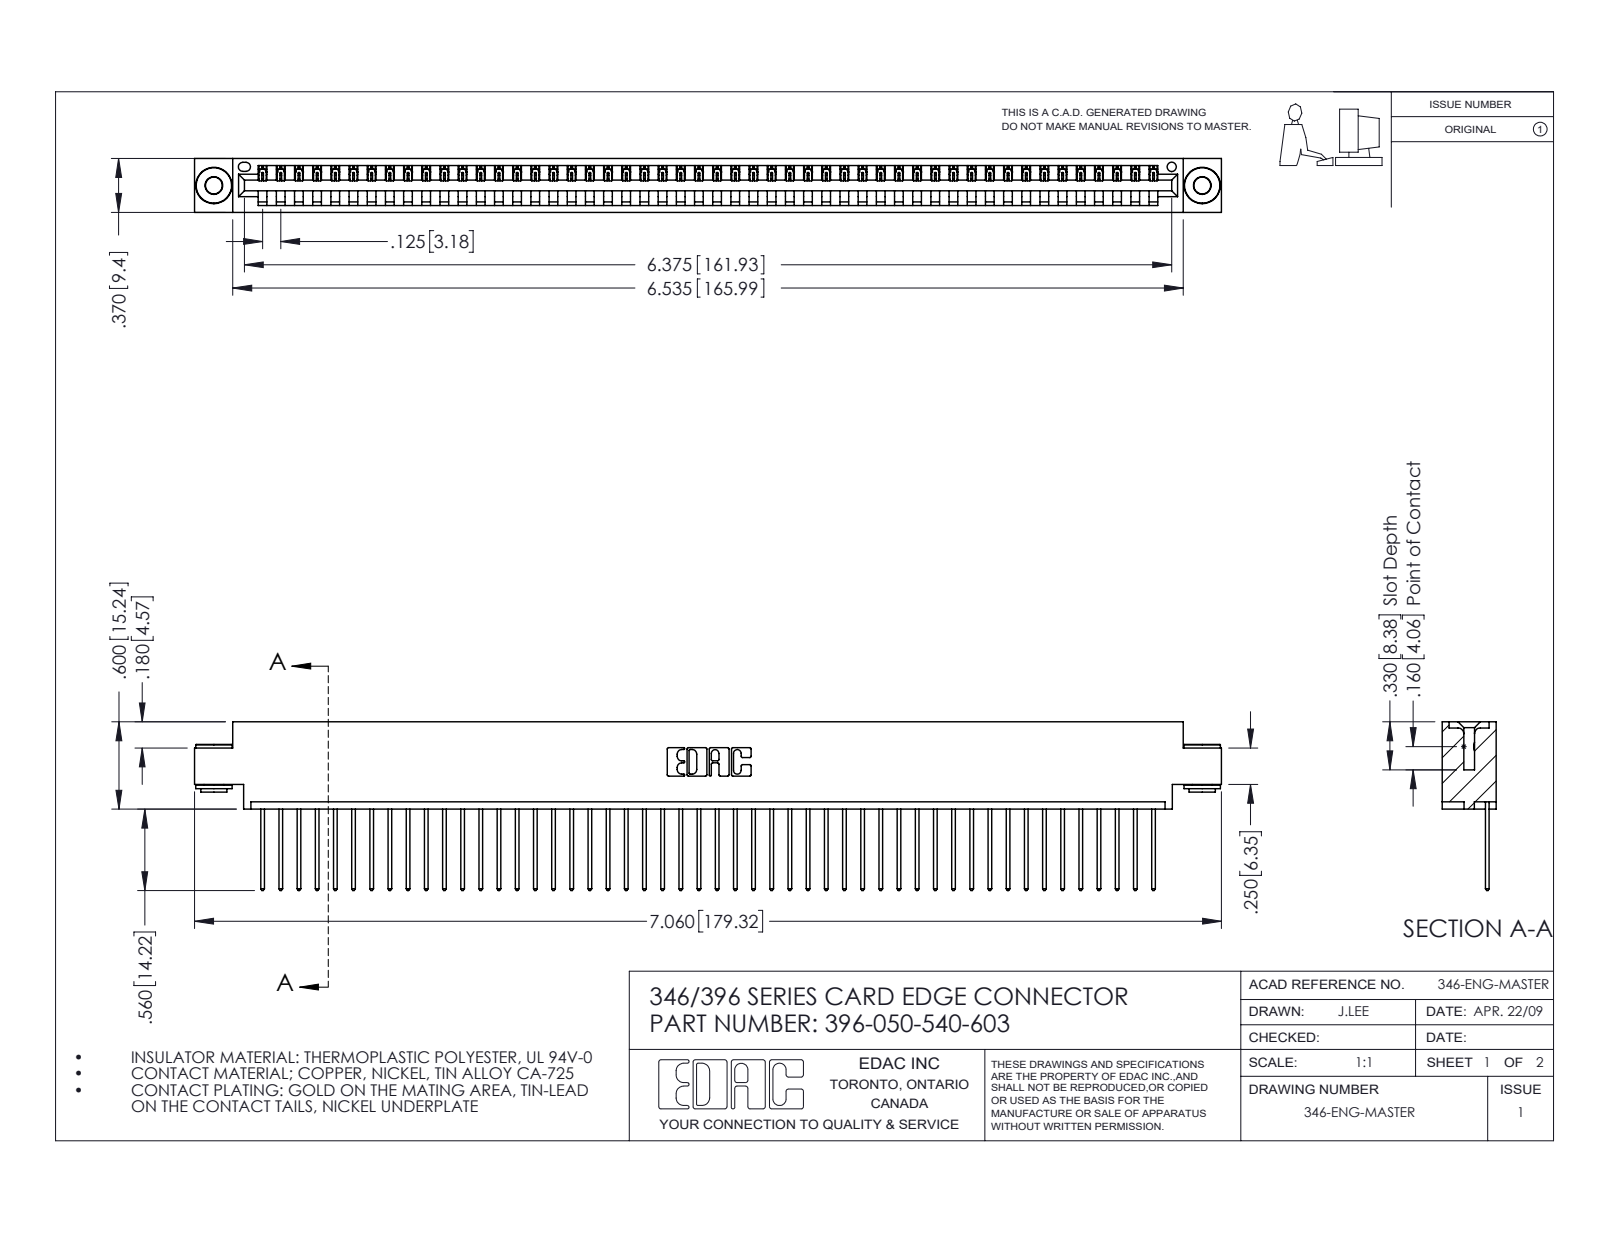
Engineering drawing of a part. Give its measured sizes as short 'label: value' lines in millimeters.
name: 345-250-002_345-250-002-102; 346 Part_0.170 Offset - 0.156 Dia-TH; 396-050-540-603; 345-292-001_345-293-140
written by: SolidWorks 2016 (CONFIG_CONTROL_DESIGN)
unit: mm
bodies: 53 solids, 3064 faces (2090 planar, 966 cylindrical, 8 other)
size: 179.3 × 29.5 × 9.4
volume: 17 160 mm³; area: 22 400 mm²
holes: 2× ⌀2.9, 2× ⌀4, 1× ⌀1.6
bosses: 2× ⌀6.4, 2× ⌀4.6, 2× ⌀3.5
rounds: 100× R0.2, 100× R0.3, 22× R0.3, 6× R0.2, 6× R0.8, 3× R0.7, 2× R0.8, 2× R1
face distances: 1.2, 8.2, 9.4, 6.4, 0.6, 1.8, 7.6, 3.8, 5.6, 2.5
hole spacings: 6.2, 167.3, 172.6
